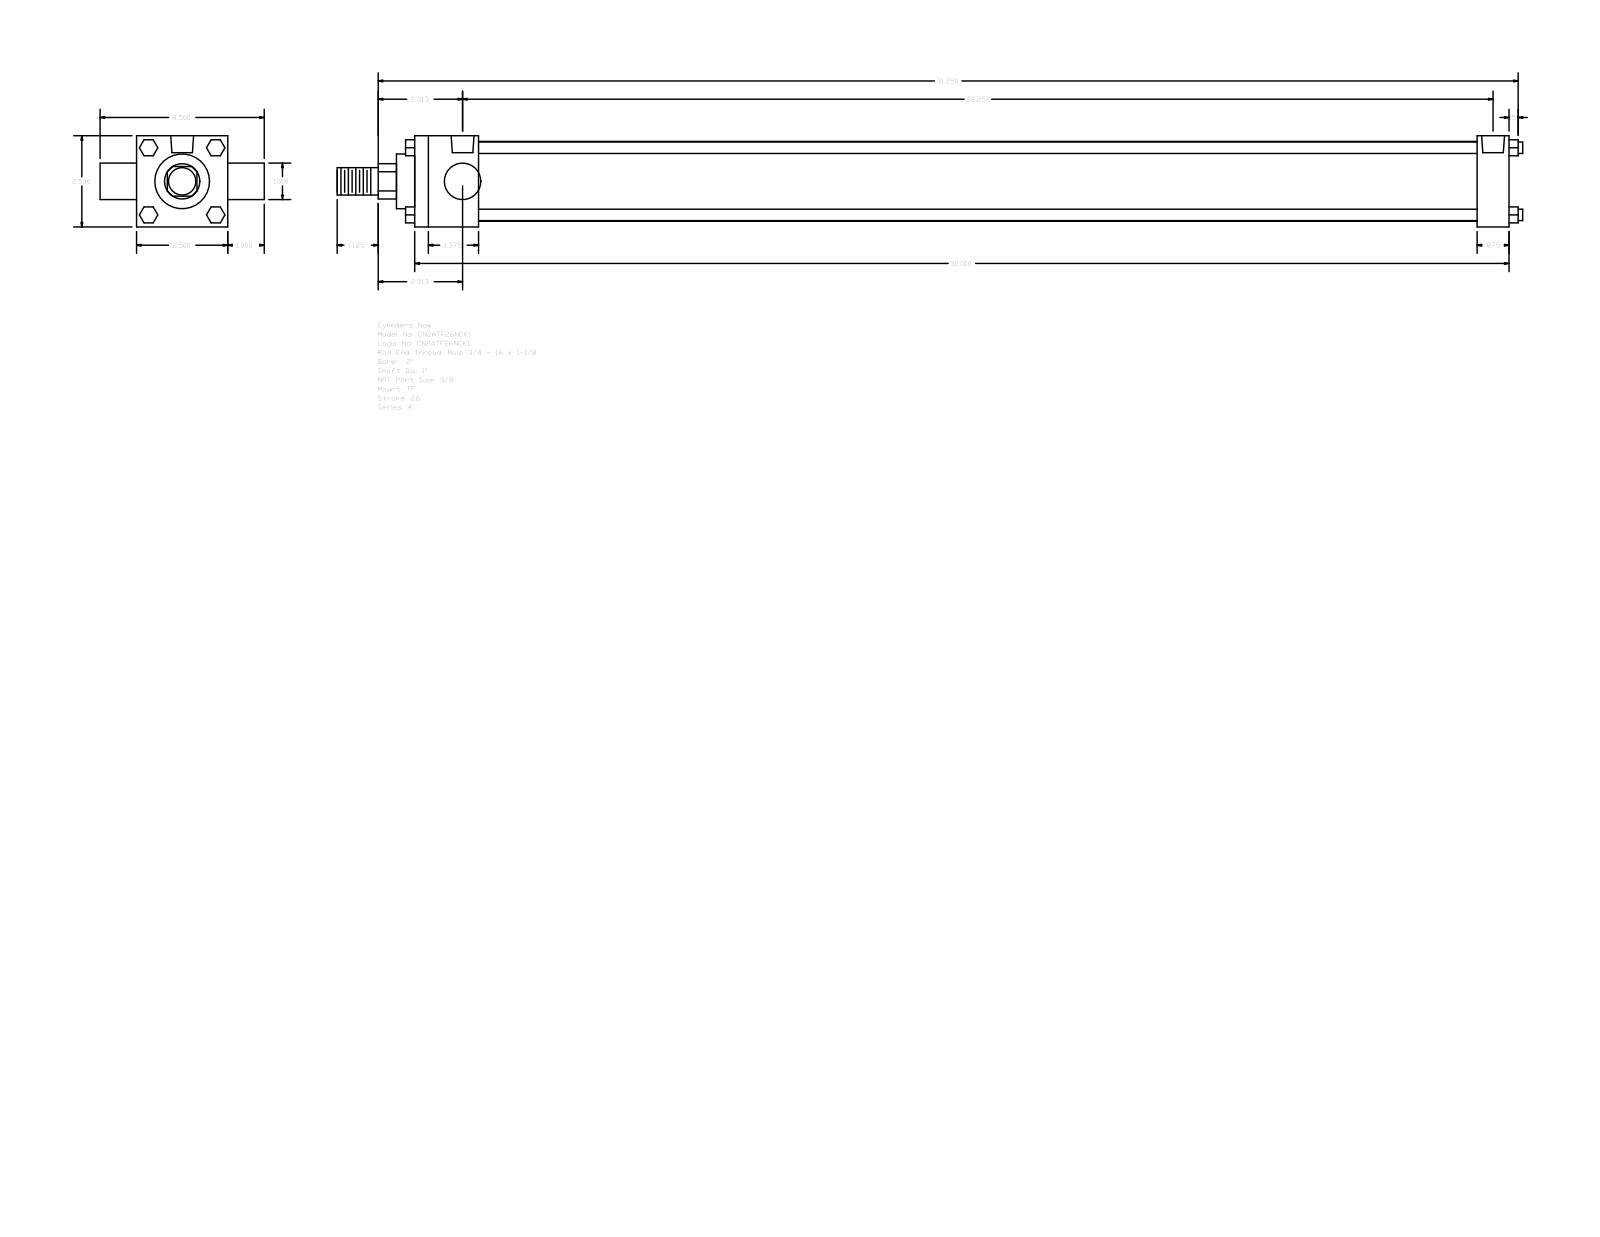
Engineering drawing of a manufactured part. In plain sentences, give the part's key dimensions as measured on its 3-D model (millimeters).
The part is named "A_TF__0200_1". Its 3-D file was written by "GSSL Pune (CONFIG_CONTROL_DESIGN)". It is 0 solids with 120 faces: 92 planar, 28 cylindrical and 0 other. Overall it measures 825.5 by 114.3 by 63.5 millimeters. Round holes: 3 of diameter 5.56, 2 of diameter 15.93. Round bosses or shafts: 4 of diameter 7.94, 2 of diameter 25.4, 1 of diameter 55.63, 1 of diameter 38.1, 1 of diameter 19.05. Partial cylindrical surfaces (rounded edges, fillets, slot ends): 1 of radius 12.29. The main face-to-face distances are 63.5, 762, 44.45, 739.77, 695.32, 717.55, 22.23, 25.4, 88.9, 774.7. The hole center spacings are 1.59, 3.98, 711.98, 713.57, 715.96, 717.55.
